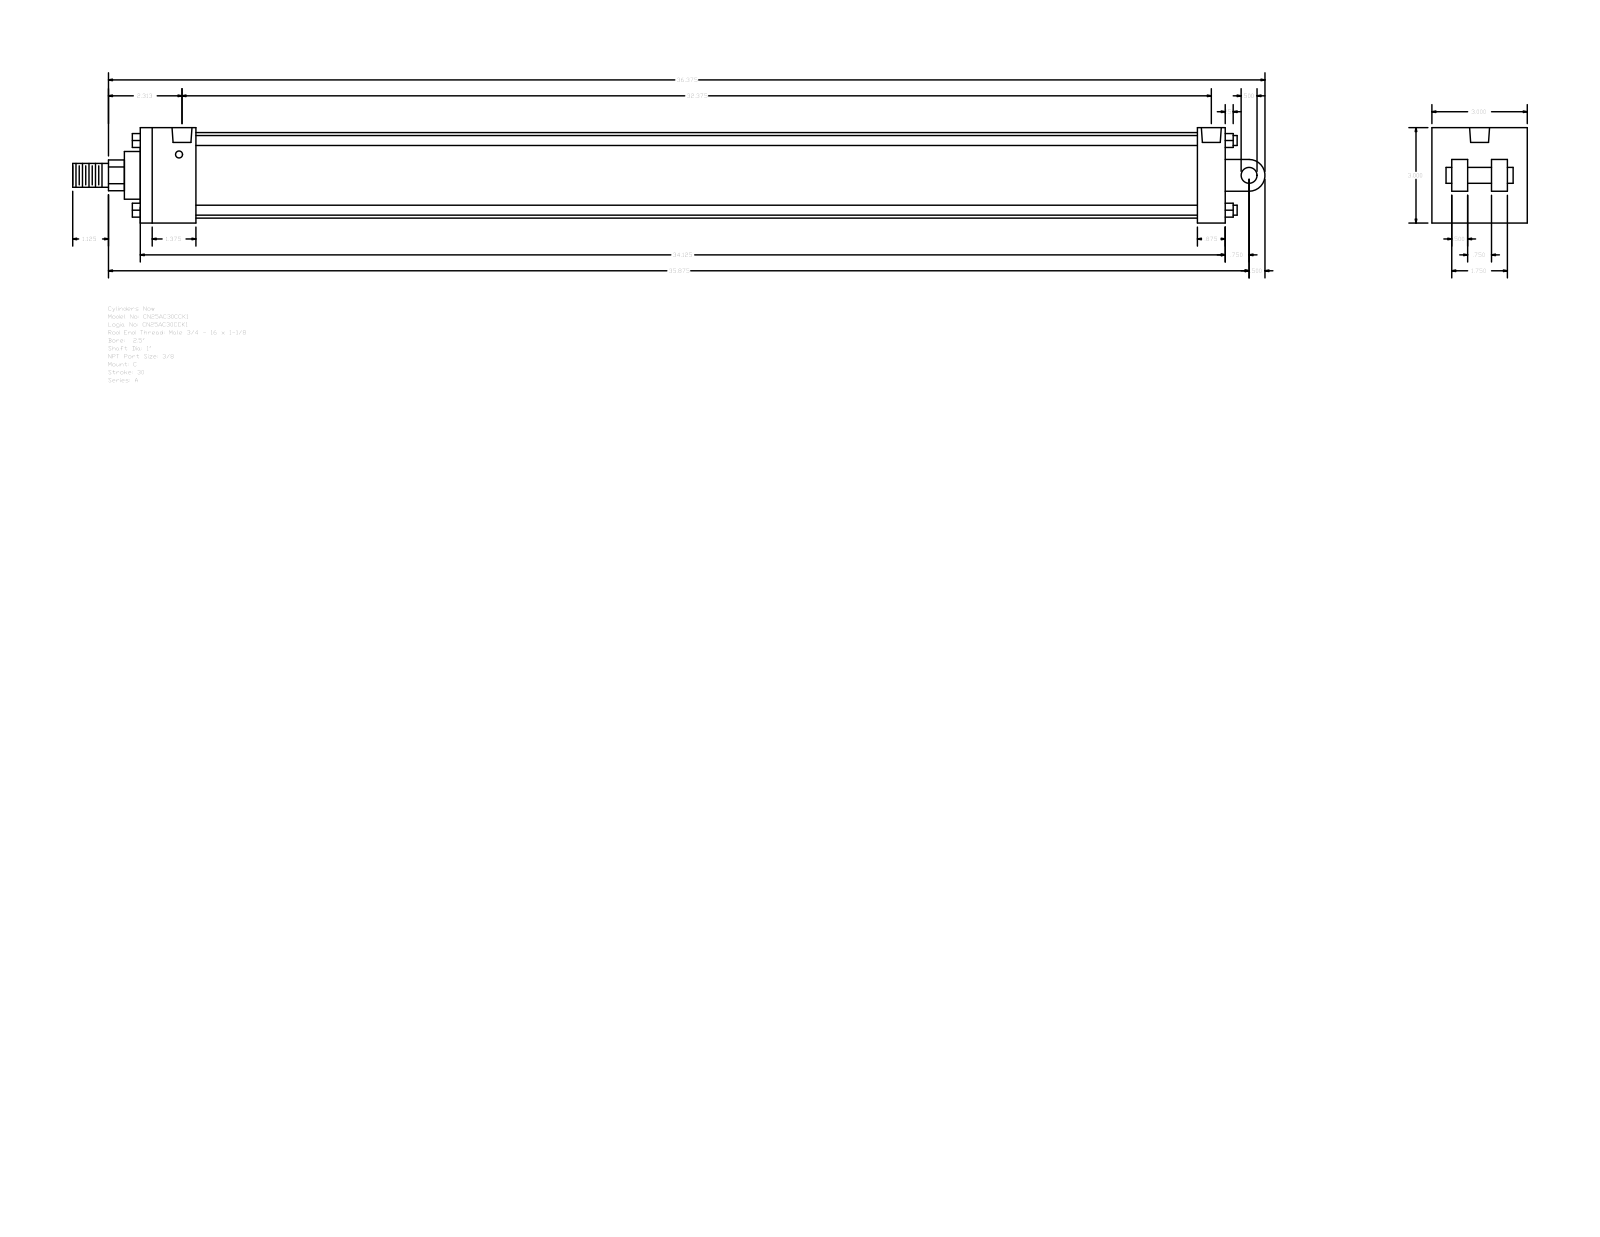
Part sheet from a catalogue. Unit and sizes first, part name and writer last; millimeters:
Units: millimetres
Overall size (bounding box): 952.5 × 76.2 × 76.2
Round holes (diameter × count): ⌀5.56 ×4, ⌀15.93 ×2
Round bosses / shafts (diameter × count): ⌀7.94 ×4, ⌀68.33 ×1, ⌀38.1 ×1, ⌀25.4 ×1, ⌀19.05 ×1, ⌀12.7 ×1
Partial cylindrical surfaces — rounded edges, fillets, slot ends (radius × count): R12.29 ×1, R12.7 ×1
Main face-to-face distances: 76.2, 866.77, 12.7, 44.45, 844.55, 800.1, 822.32, 22.22, 15.87, 25.4
Hole centre spacings: 2.38, 824.7, 827.08, 822.32
Bodies: 0 solids, 135 faces (102 planar, 33 cylindrical, 0 other)
Part name (STEP PRODUCT): A_C__0250_1
STEP written by: GSSL Pune (CONFIG_CONTROL_DESIGN)
